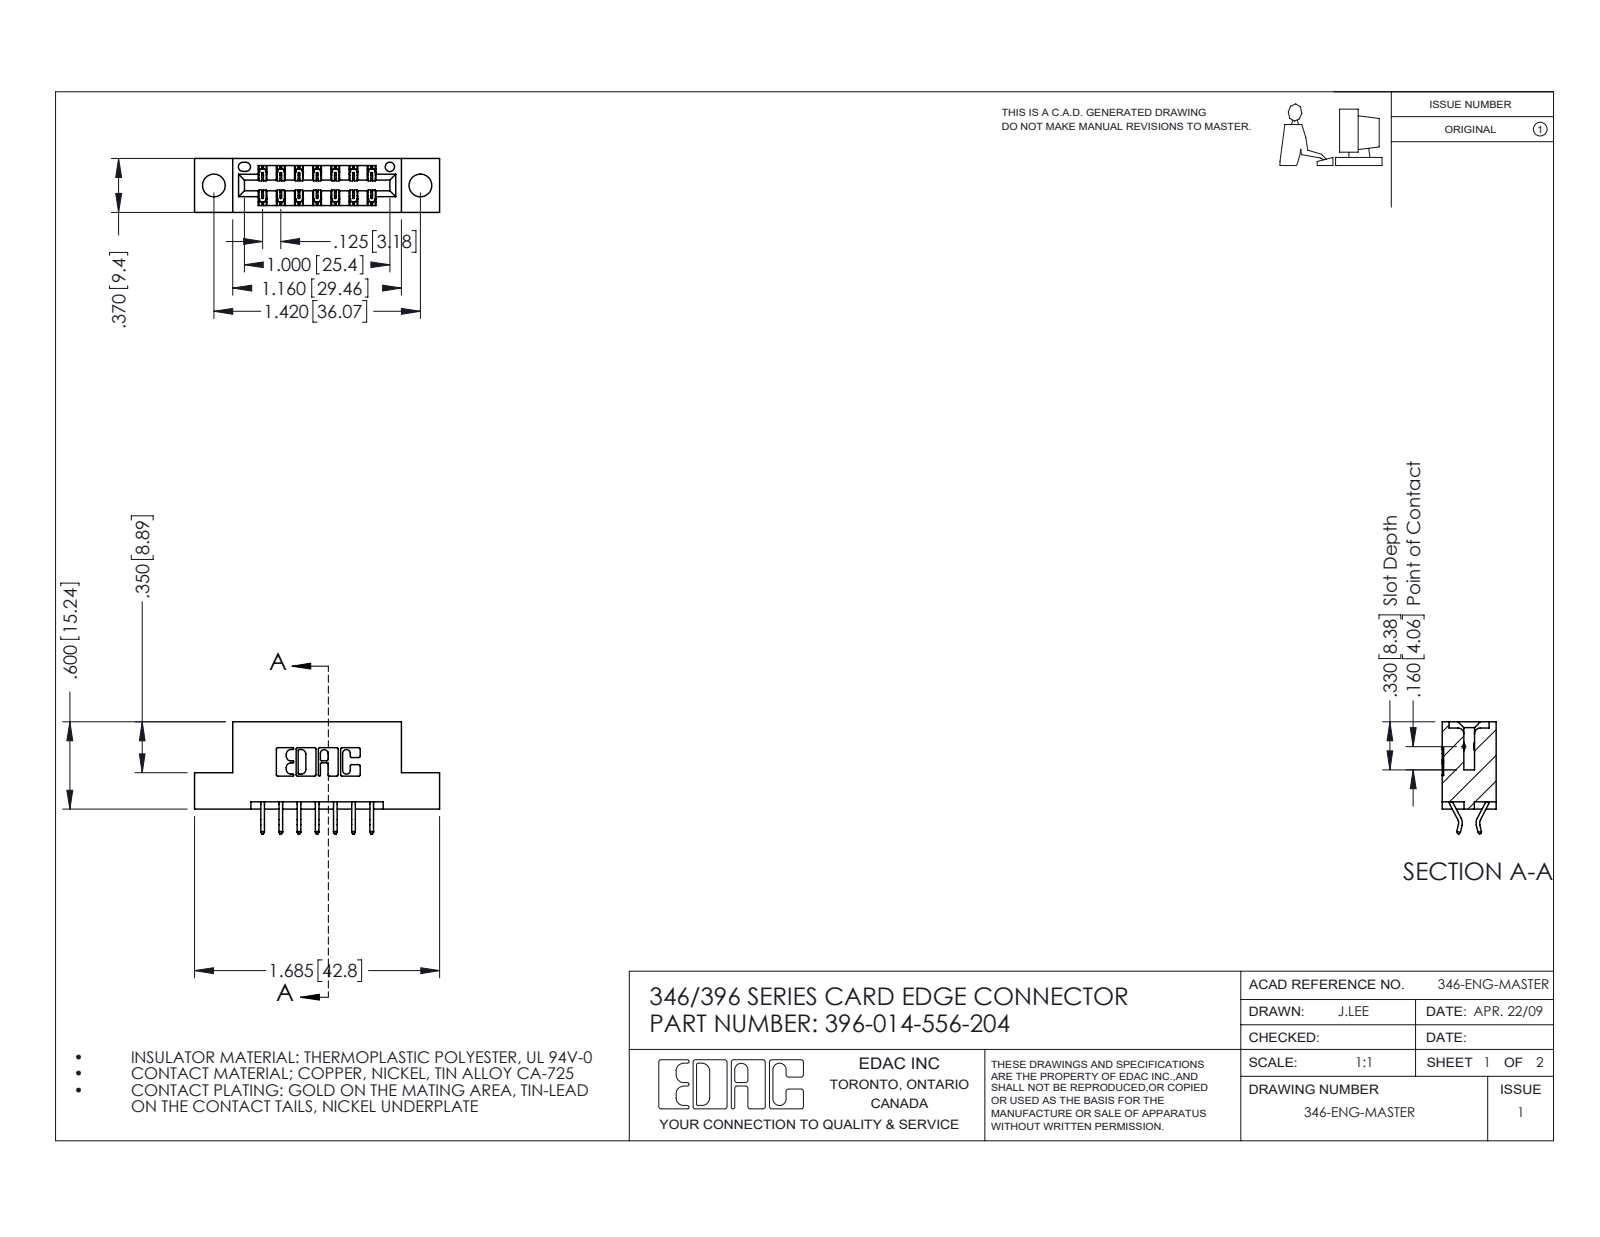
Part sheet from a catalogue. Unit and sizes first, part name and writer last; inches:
Units: inches
Overall size (bounding box): 1.685 × 0.77 × 0.37
Round holes (diameter × count): ⌀0.156 ×2, ⌀0.064 ×1
Partial cylindrical surfaces — rounded edges, fillets, slot ends (radius × count): R0.01 ×22, R0.006 ×21, R0.007 ×6, R0.031 ×6, R0.026 ×3, R0.01 ×2, R0.014 ×2, R0.022 ×2
Main face-to-face distances: 0.25, 0.37, 0.048, 0.322, 0.025, 0.148, 0.222, 0.1, 0.174, 0.125
Hole centre spacings: 0.246, 1.217, 1.42
Volume: 0.233 in³ · Surface area: 6.962 in²
Bodies: 15 solids, 934 faces (622 planar, 312 cylindrical, 0 other)
Part name (STEP PRODUCT): 346 Part_Flush Mounting Lugs - 0.156 Dia-TH; 345-292-001_556 Tail; 396-014-556-204
STEP written by: SolidWorks 2016 (CONFIG_CONTROL_DESIGN)
